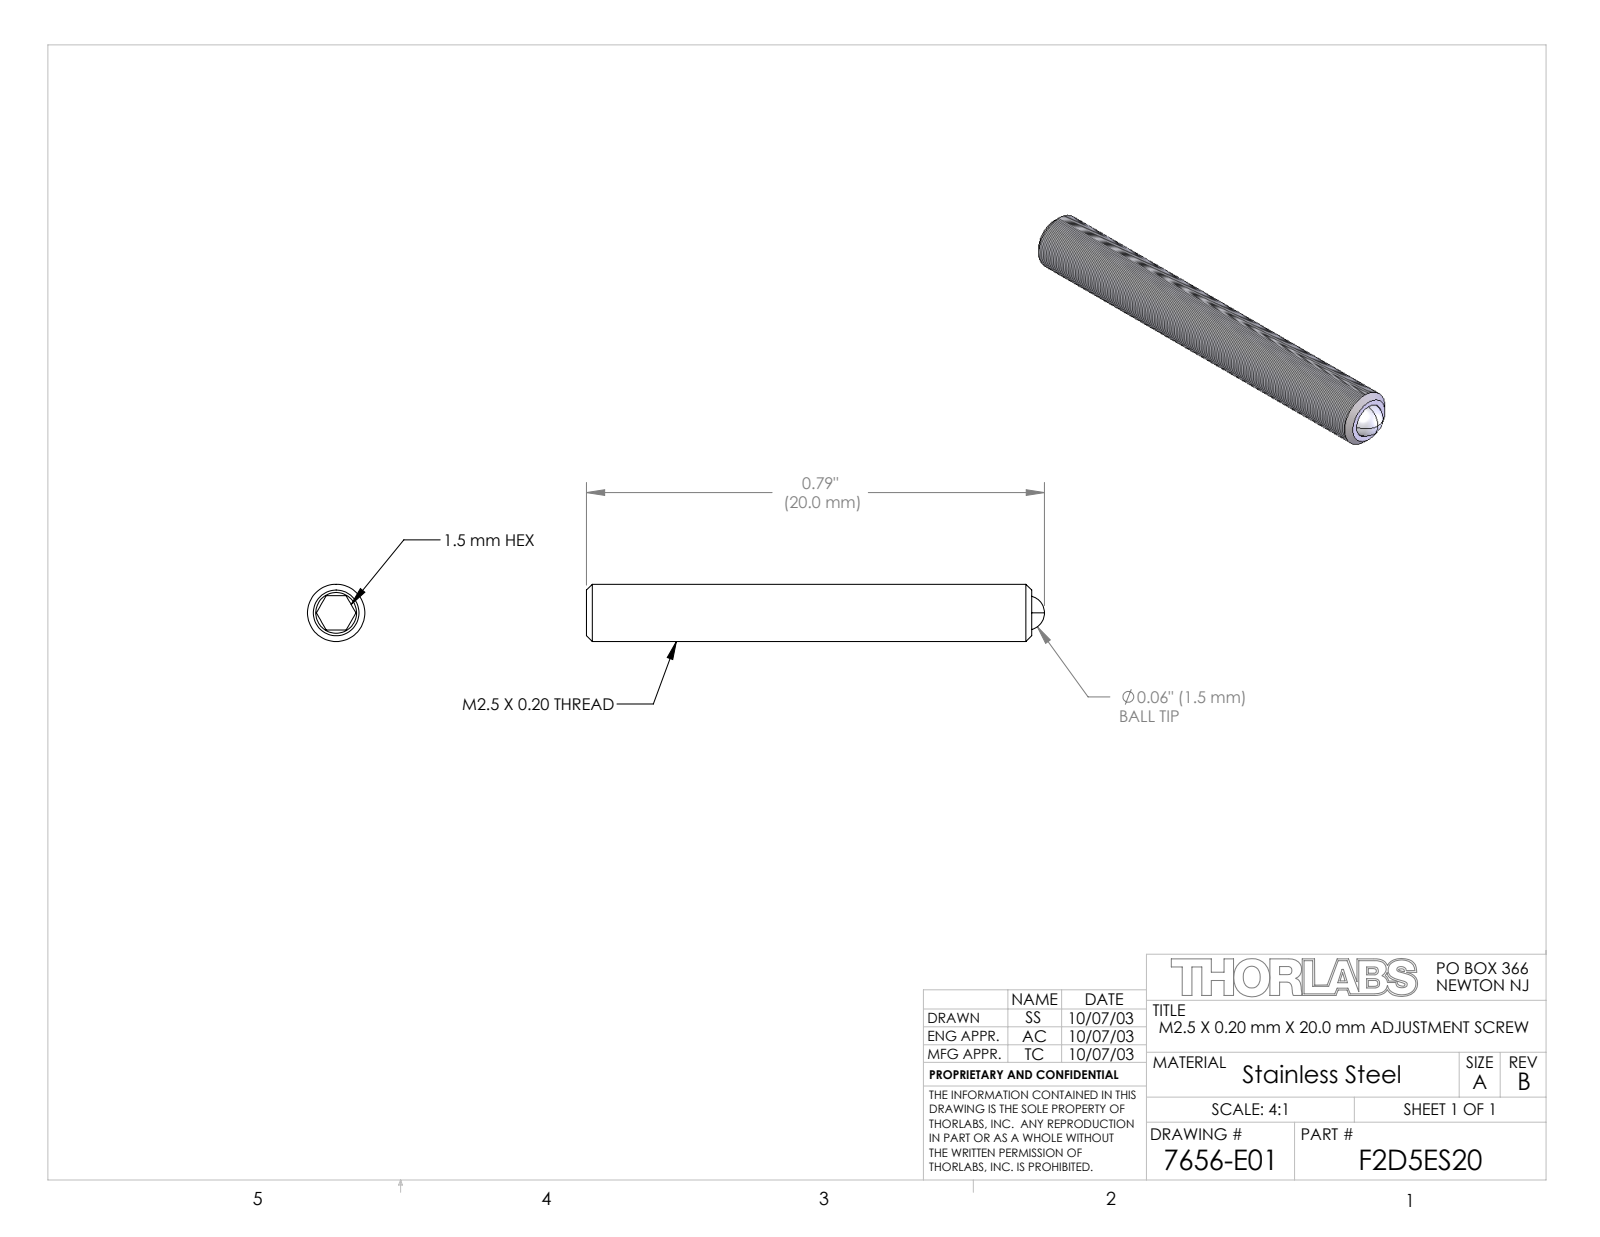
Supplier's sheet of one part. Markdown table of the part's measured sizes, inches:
| quantity | value |
| --- | --- |
| part name | 7656-E0W |
| STEP written by | SolidWorks 2011 (AUTOMOTIVE_DESIGN) |
| units | inches |
| bodies | 2 solids, 25 faces (9 planar, 4 cylindrical, 12 other) |
| overall size | 0.809 × 0.098 × 0.098 |
| volume | 0.006 in³ |
| surface area | 0.295 in² |
| round holes (diameter × count) | 0.059 × 1 |
| round bosses / shafts (diameter × count) | 0.098 × 1 |
| main face-to-face distances | 0.059, 0.667, 0.787, 0.12 |
